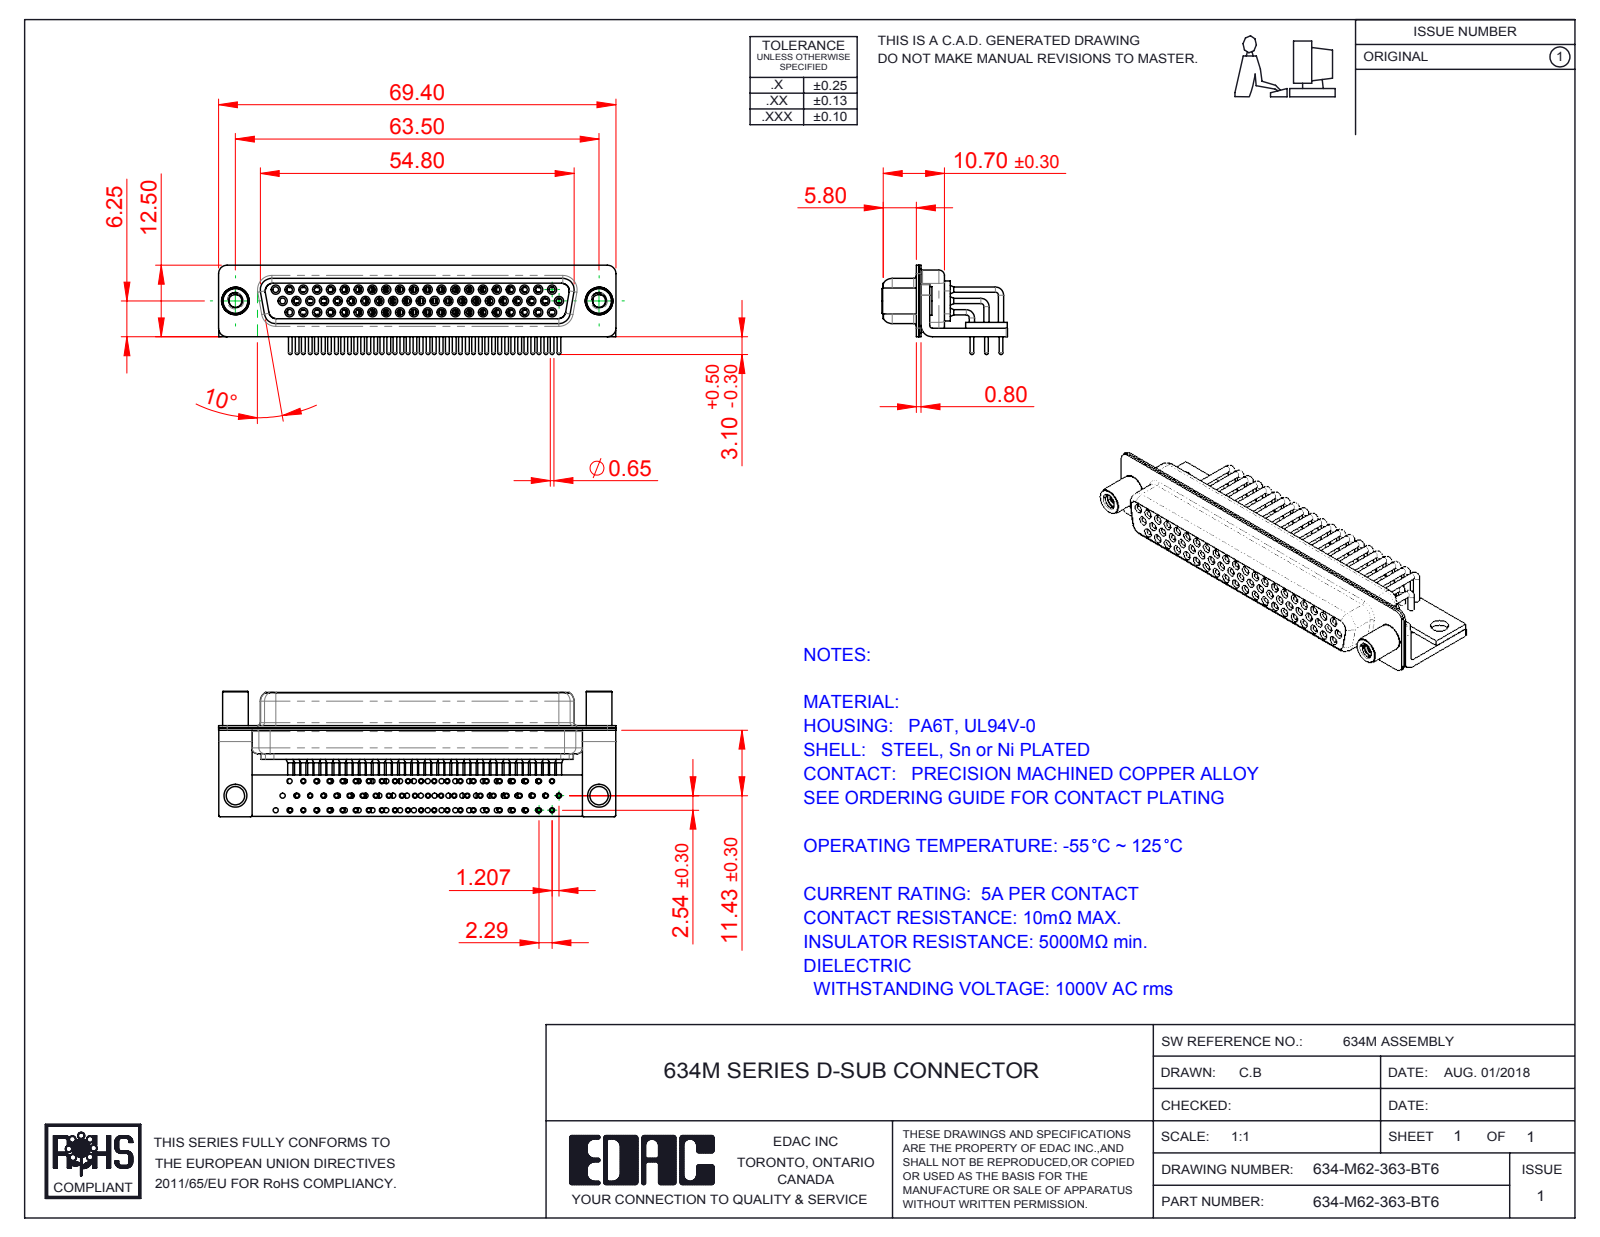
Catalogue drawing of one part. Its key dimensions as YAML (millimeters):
part_name: "634M Contact Row 3; 634M Housing_62 Contacts; 634M Stabilizer Bracket; 634M Shell Front_62 Contacts (+6 more)"
step_written_by: "SolidWorks 2016 (CONFIG_CONTROL_DESIGN)"
units: millimeters
bodies: {solids: 70, faces: 3789, planar: 1025, cylindrical: 1751, other: 1013}
overall_size: [69.4, 21.9, 15.6]
volume: 6258
surface_area: 20041
round_holes:
  - {diameter: 0.9, count: 62}
  - {diameter: 1, count: 62}
  - {diameter: 1.1, count: 62}
  - {diameter: 1.7, count: 62}
  - {diameter: 1.8, count: 62}
  - {diameter: 2, count: 62}
  - {diameter: 2.26, count: 2}
  - {diameter: 3.2, count: 2}
  - {diameter: 4, count: 2}
  - {diameter: 4.8, count: 2}
round_bosses_or_shafts:
  - {diameter: 0.9, count: 118}
  - {diameter: 1.6, count: 62}
  - {diameter: 1.5, count: 62}
  - {diameter: 0.65, count: 62}
  - {diameter: 2, count: 56}
  - {diameter: 5, count: 2}
  - {diameter: 4.9, count: 2}
  - {diameter: 4.5, count: 2}
partial_cylinders:
  - {radius: 0.25, count: 16}
  - {radius: 1.5, count: 16}
  - {radius: 2, count: 13}
  - {radius: 1.35, count: 8}
  - {radius: 1.6, count: 8}
  - {radius: 0.5, count: 5}
  - {radius: 0.6, count: 4}
  - {radius: 0.65, count: 4}
face_to_face_distances: [0.4, 2.3, 1.9, 1, 8.5, 1.45, 8.95, 0.85, 0.8, 6.2]
hole_center_spacings: [7.24, 2.41, 9.65, 4.83, 14.48, 16.89, 2.81, 2.32]
